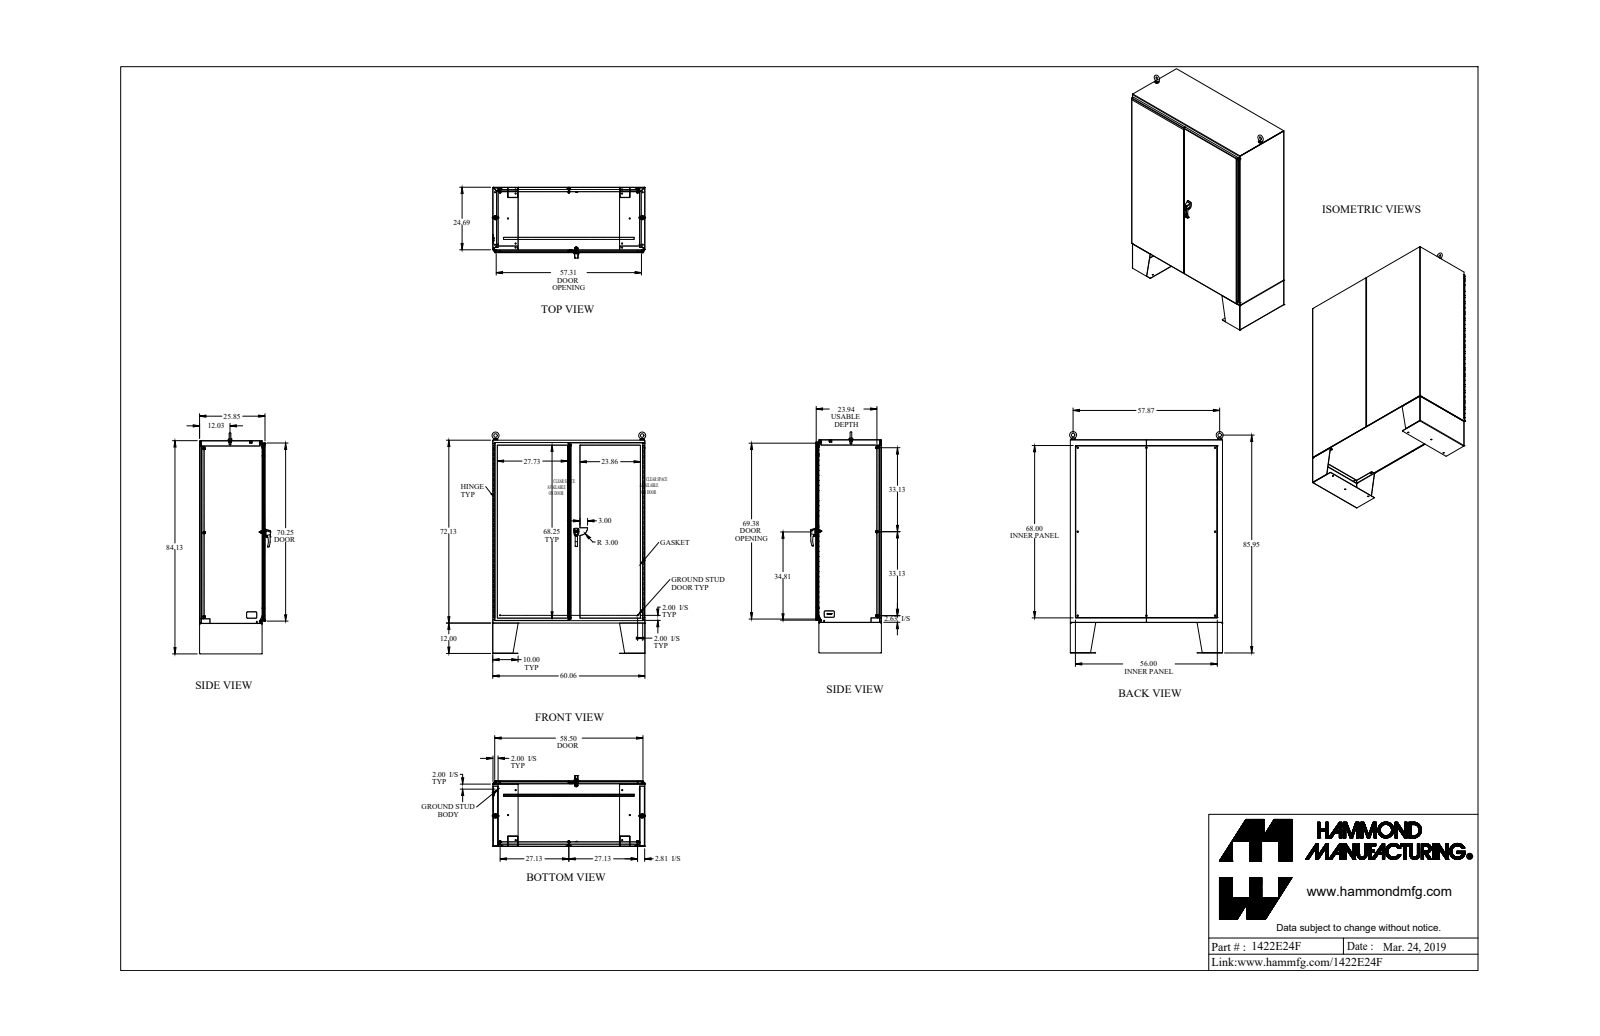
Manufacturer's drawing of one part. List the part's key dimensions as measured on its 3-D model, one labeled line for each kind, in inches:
Part name (STEP PRODUCT): 1422E24F_Default
STEP written by: SolidWorks 2019 (CONFIG_CONTROL_DESIGN)
Units: inches
Bodies: 92 solids, 2997 faces (1372 planar, 1378 cylindrical, 247 other)
Overall size (bounding box): 87.778 × 61.121 × 27.963
Volume: 2 478 in³ · Surface area: 46 991 in²
Round holes (diameter × count): ⌀0.304 ×24, ⌀0.437 ×14, ⌀0.307 ×9, ⌀0.563 ×8, ⌀0.445 ×6, ⌀0.11 ×2, ⌀0.25 ×2, ⌀0.257 ×2, ⌀0.28 ×2, ⌀0.281 ×2, ⌀0.313 ×2, ⌀0.39 ×2
Round bosses / shafts (diameter × count): ⌀1 ×10, ⌀0.65 ×8, ⌀0.375 ×8, ⌀0.33 ×8, ⌀0.281 ×6, ⌀0.25 ×4, ⌀1.75 ×2, ⌀1.5 ×2
Partial cylindrical surfaces — rounded edges, fillets, slot ends (radius × count): R0.048 ×32, R0.143 ×32, R0.125 ×22, R0.018 ×16, R0.06 ×14, R0.116 ×12, R0.187 ×9, R0.05 ×8
Main face-to-face distances: 0.095, 0.125, 25.753, 25.628, 59.968, 25.723, 25.848, 0.125, 1.687, 24.036
Hole centre spacings: 6, 12, 58.7, 59.613, 18, 61.104, 24, 63.132
